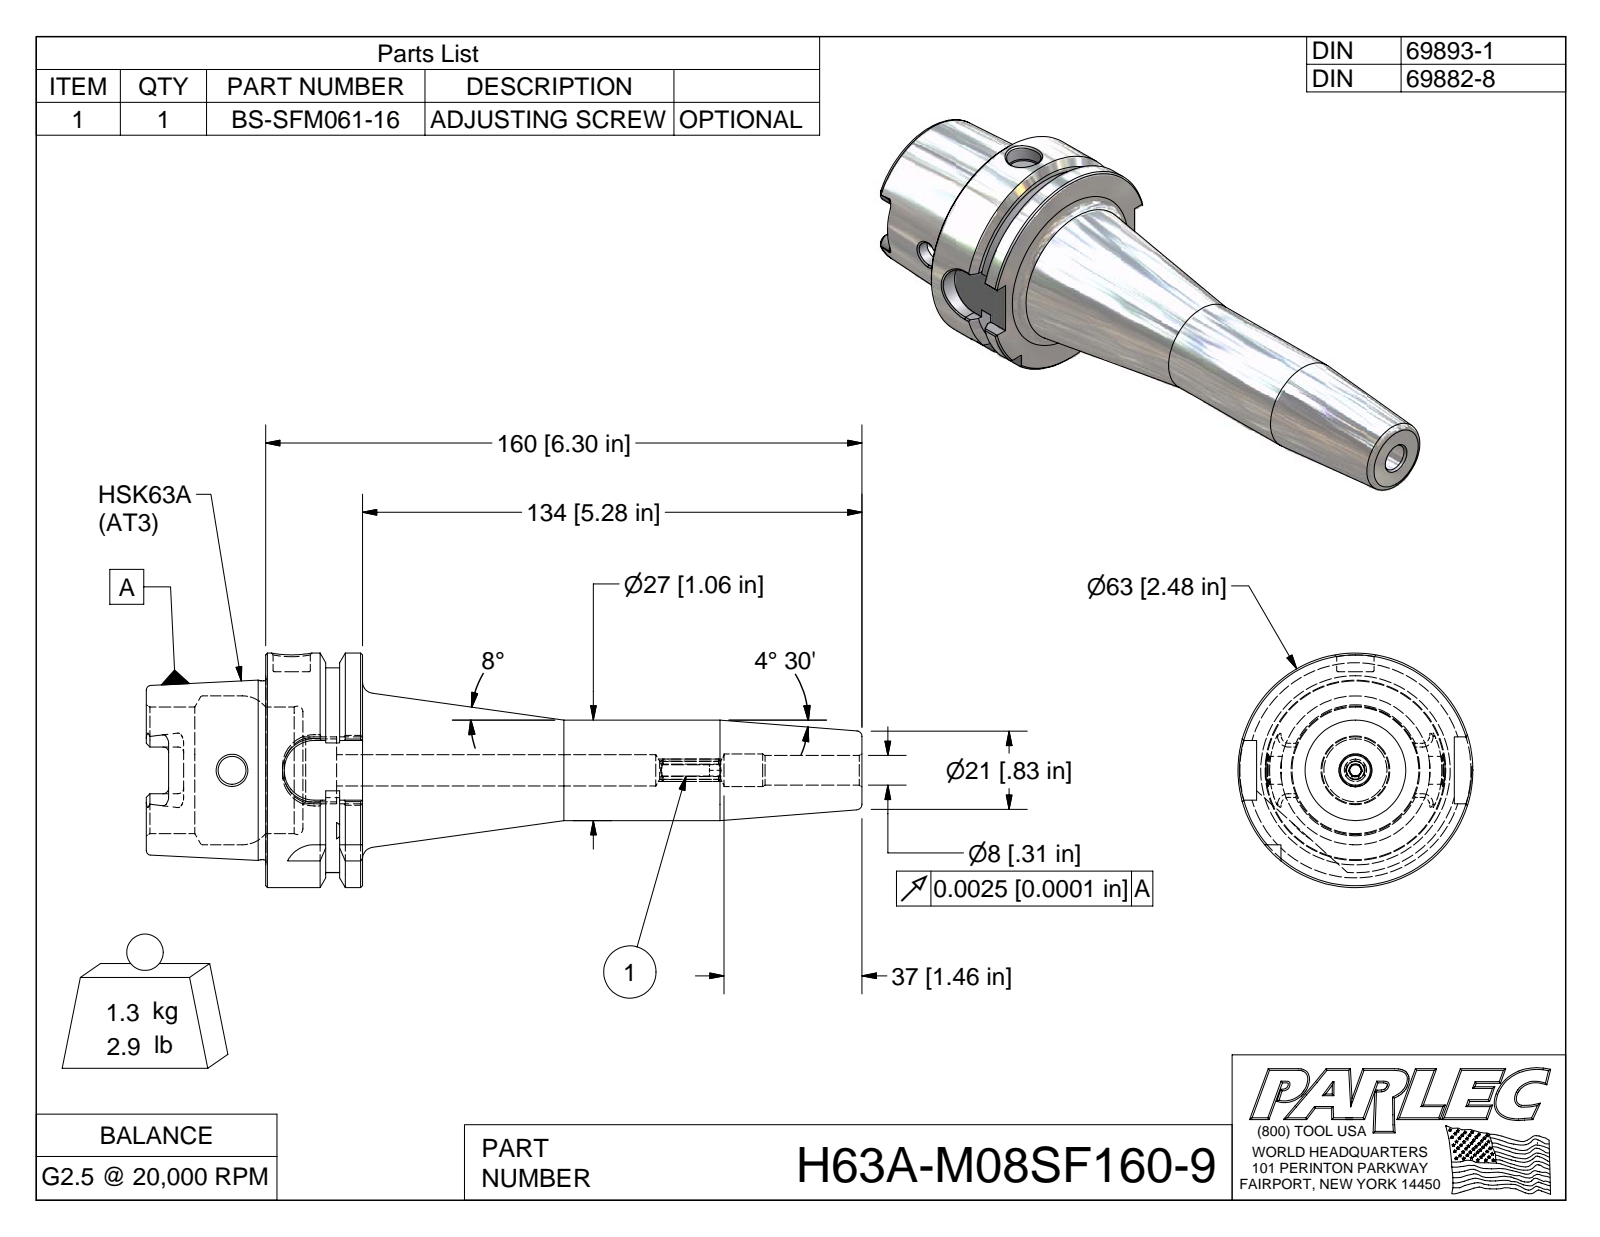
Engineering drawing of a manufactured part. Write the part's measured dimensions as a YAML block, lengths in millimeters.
part_name: "H63A-M08SF160-9; H63A-M08SF160-9-1; BS-SFM061-16"
step_written_by: "Autodesk Inventor 2009 (AUTOMOTIVE_DESIGN)"
units: millimeters
bodies: {solids: 2, faces: 165, planar: 59, cylindrical: 35, other: 71}
overall_size: [192, 63, 63]
volume: 168300
surface_area: 37300
round_holes:
  - {diameter: 7.5, count: 1}
  - {diameter: 8, count: 1}
  - {diameter: 8.7, count: 1}
  - {diameter: 10, count: 1}
  - {diameter: 16.9, count: 1}
  - {diameter: 34, count: 1}
  - {diameter: 40, count: 1}
round_bosses_or_shafts:
  - {diameter: 63, count: 1}
  - {diameter: 48, count: 1}
  - {diameter: 27, count: 1}
partial_cylinders:
  - {radius: 1.5, count: 6}
  - {radius: 2.9, count: 4}
  - {radius: 8, count: 4}
  - {radius: 3, count: 1}
  - {radius: 27.5, count: 1}
face_to_face_distances: [26, 6.1, 9.9, 10, 16, 32, 42, 58, 48.1, 16.1]
